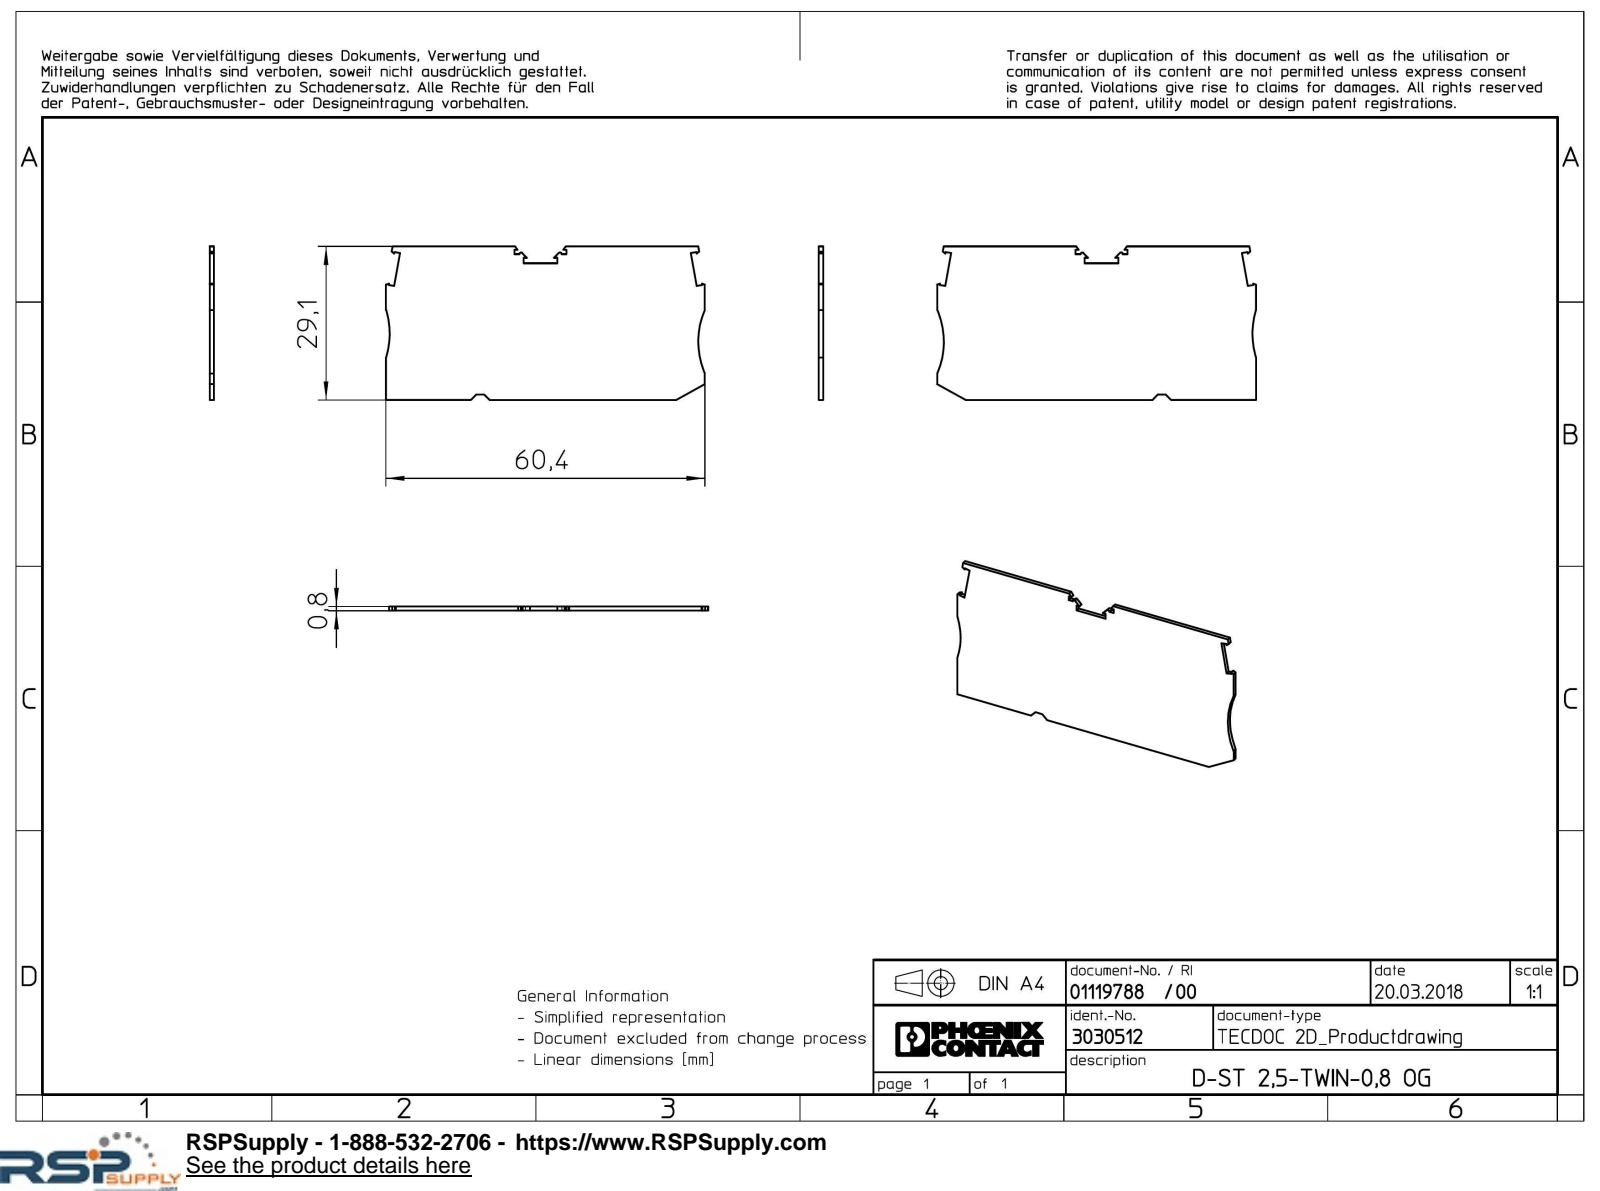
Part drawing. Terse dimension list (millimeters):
name: D-ST_2.5-TWIN-0.8-Select
written by: Creo Elements/Direct Modeling 18.1I 14-Aug-2016 (C) Parametric Technology GmbH (AUTOMOTIVE_DESIGN)
unit: mm
bodies: 1 solid, 49 faces (45 planar, 4 cylindrical, 0 other)
size: 60.4 × 29.05 × 0.8
volume: 1 341 mm³; area: 3 508 mm²
rounds: 2× R0.3, 2× R15
face distances: 0.8, 29.05, 60.4, 25.85, 3.2, 6.33, 27.6, 1.75, 1.45, 1
